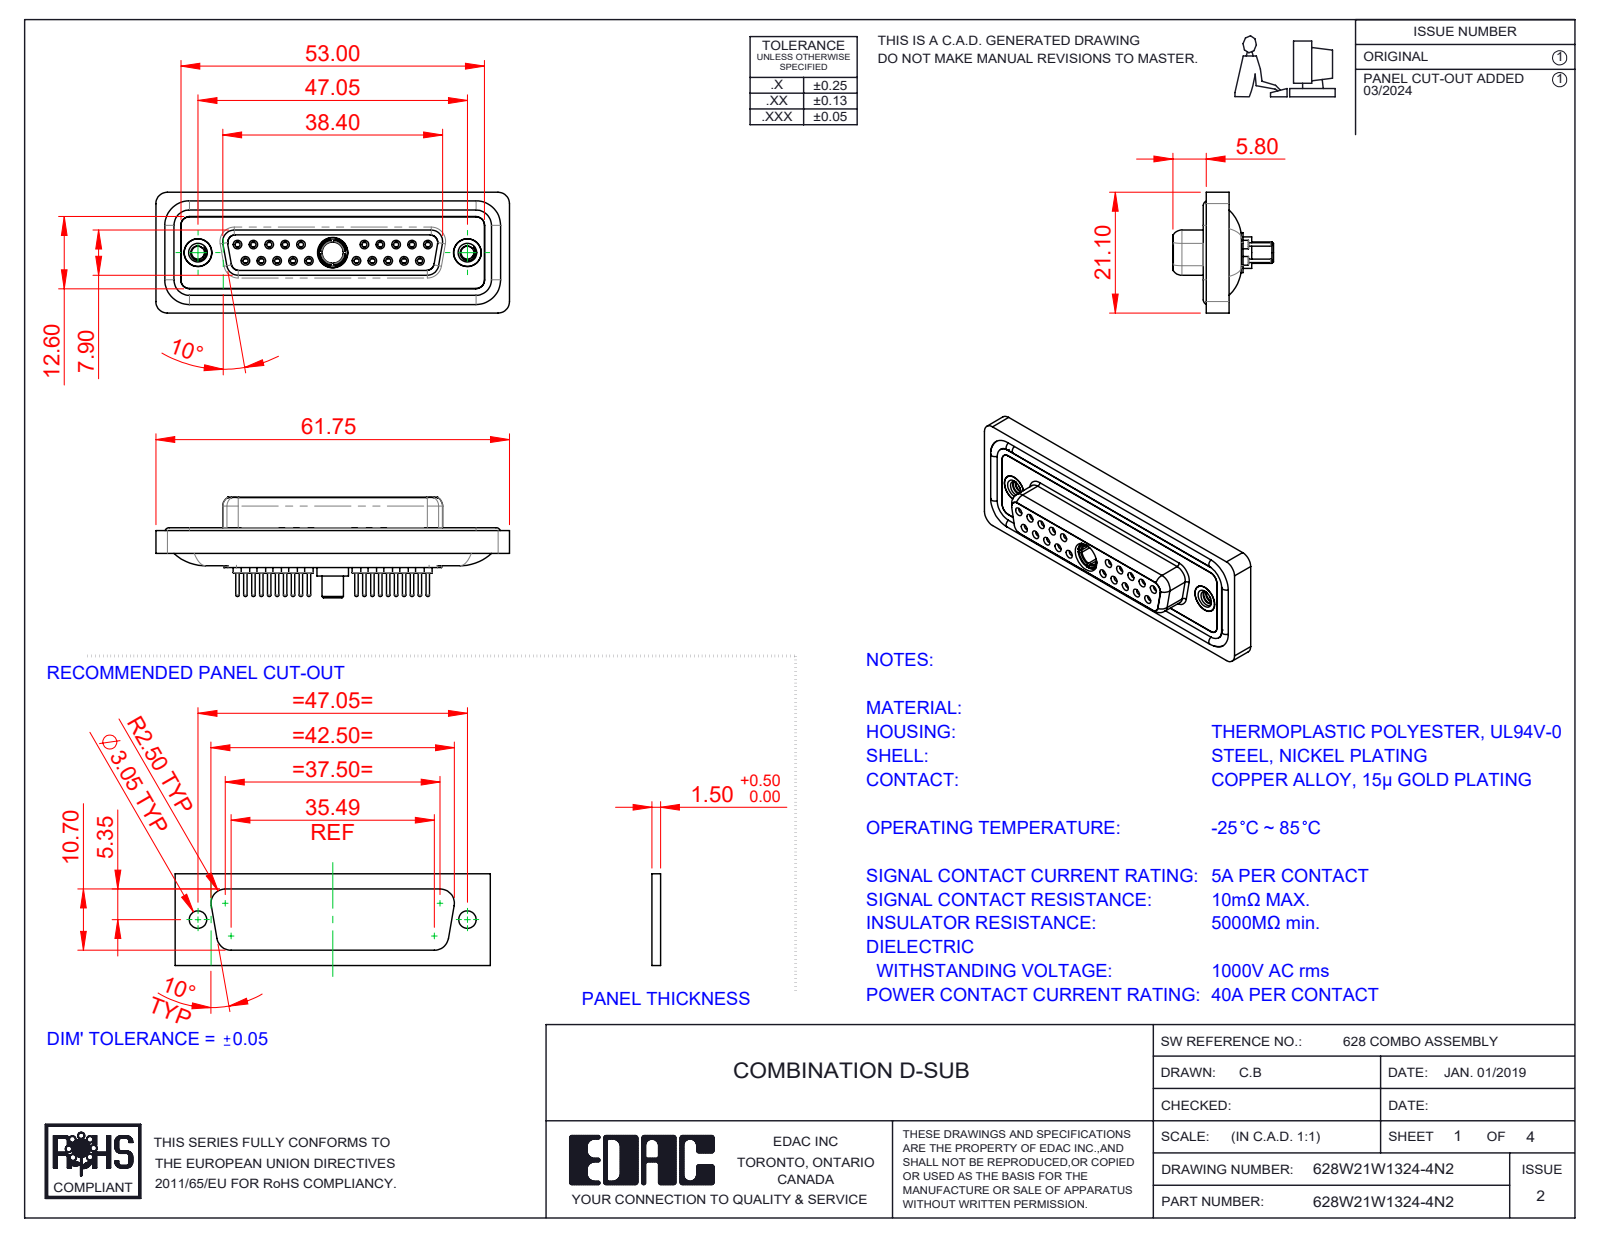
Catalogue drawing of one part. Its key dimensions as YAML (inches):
part_name: "628Combo Housing_21W1; 628Combo Waterproof Housing_25 Contacts; 628Combo Shell Front_25 Contacts; 628Combo Threaded Rivet_2 (+5 more)"
step_written_by: "SolidWorks 2023 (CONFIG_CONTROL_DESIGN)"
units: inches
bodies: {solids: 29, faces: 1560, planar: 434, cylindrical: 591, other: 535}
overall_size: [2.431, 0.831, 0.691]
volume: 0.512
surface_area: 21.72
round_holes:
  - {diameter: 0.035, count: 20}
  - {diameter: 0.043, count: 20}
  - {diameter: 0.059, count: 20}
  - {diameter: 0.079, count: 20}
  - {diameter: 0.063, count: 10}
  - {diameter: 0.067, count: 10}
  - {diameter: 0.191, count: 3}
  - {diameter: 0.089, count: 2}
  - {diameter: 0.157, count: 2}
  - {diameter: 0.159, count: 2}
  - {diameter: 0.197, count: 2}
  - {diameter: 0.146, count: 1}
round_bosses_or_shafts:
  - {diameter: 0.087, count: 20}
  - {diameter: 0.024, count: 20}
  - {diameter: 0.063, count: 14}
  - {diameter: 0.195, count: 2}
  - {diameter: 0.189, count: 2}
  - {diameter: 0.217, count: 1}
  - {diameter: 0.205, count: 1}
  - {diameter: 0.195, count: 1}
partial_cylinders:
  - {radius: 0.059, count: 22}
  - {radius: 0.079, count: 18}
  - {radius: 0.053, count: 8}
  - {radius: 0.063, count: 8}
  - {radius: 0.01, count: 4}
  - {radius: 0.02, count: 4}
  - {radius: 0.024, count: 4}
  - {radius: 0.026, count: 4}
face_to_face_distances: [0.016, 0.071, 0.293, 0.26, 0.222, 0.02, 0.063, 0.278, 0.114, 0.043]
hole_center_spacings: [0.124, 0.109, 0.218, 0.198, 0.327, 0.294, 0.654, 0.763]
